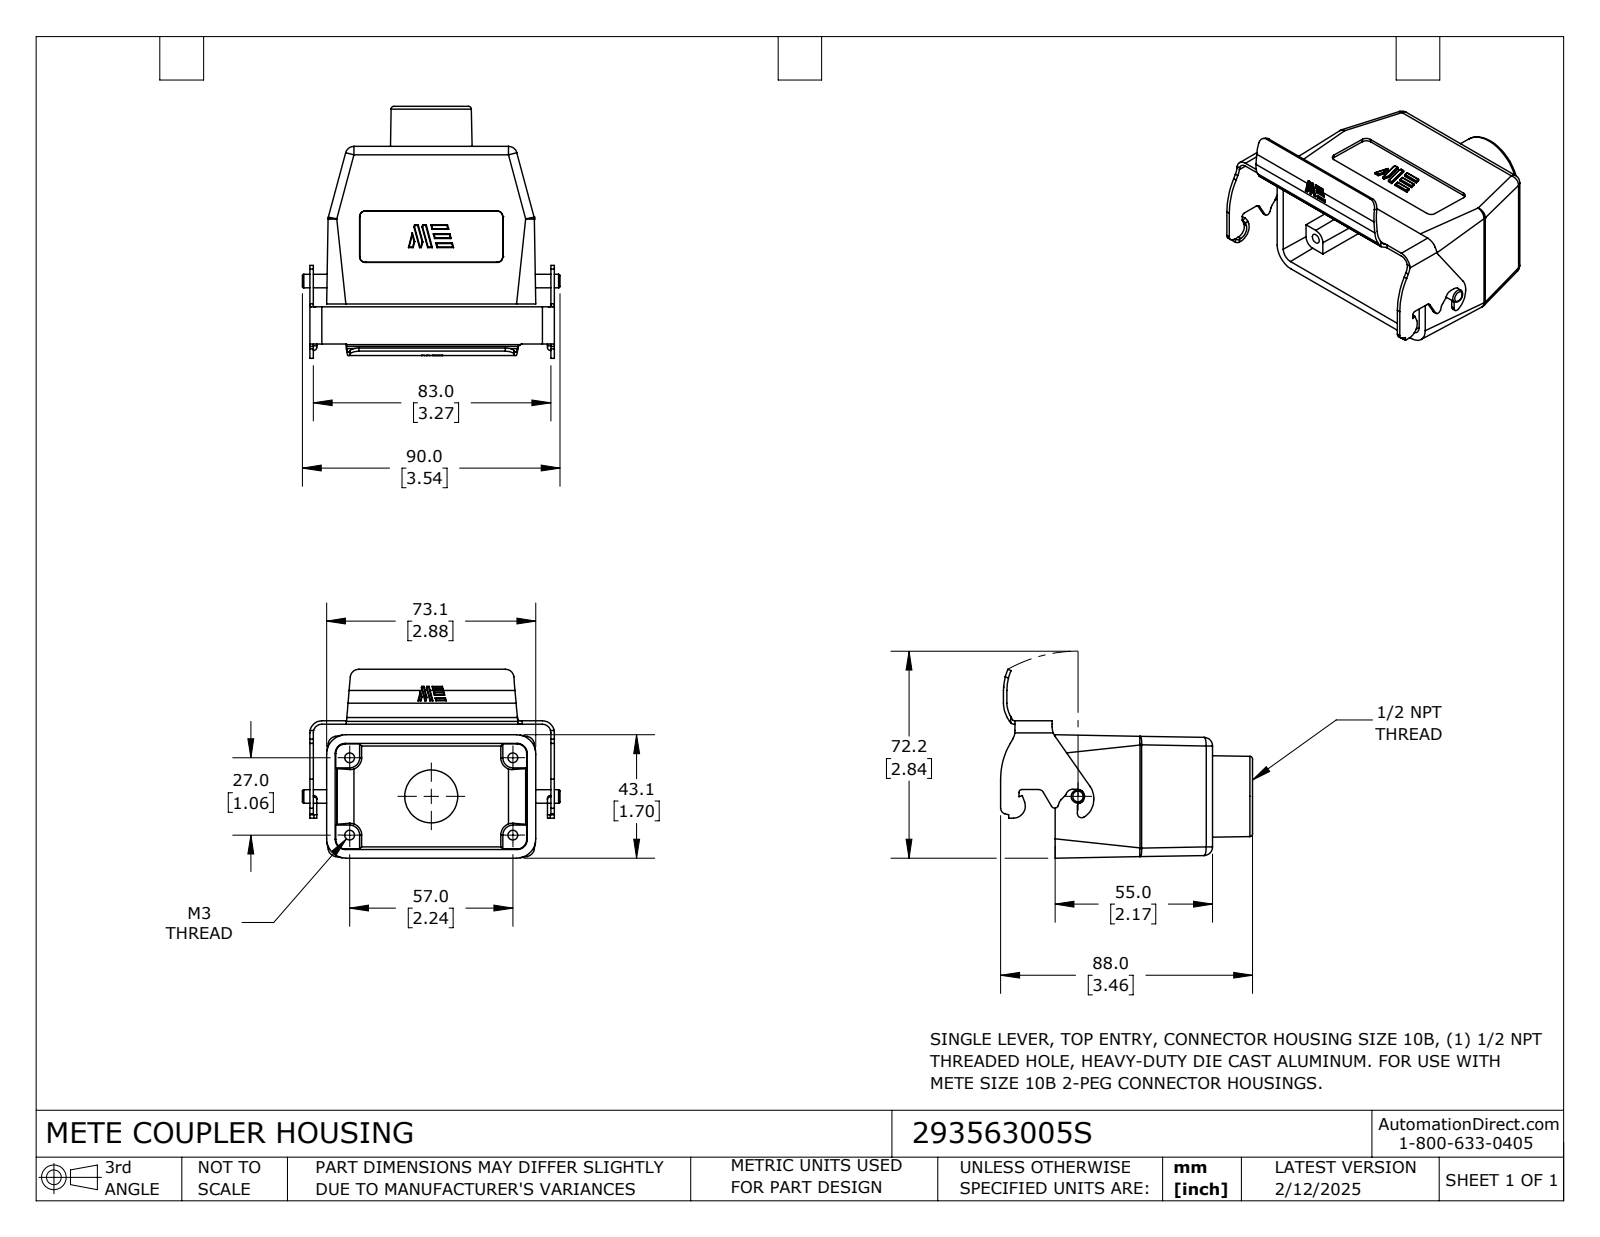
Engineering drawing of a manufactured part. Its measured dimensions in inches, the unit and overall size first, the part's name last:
Units: inches
Overall size (bounding box): 3.543 × 3.465 × 2.596
Round holes (diameter × count): ⌀0.134 ×4, ⌀0.728 ×1
Round bosses / shafts (diameter × count): ⌀0.185 ×1
Partial cylindrical surfaces — rounded edges, fillets, slot ends (radius × count): R0.008 ×55, R0.118 ×13, R0.039 ×12, R0.079 ×11, R0.098 ×5, R0.031 ×3, R0.165 ×3, R0.059 ×2
Main face-to-face distances: 0.118, 0.047, 0.04, 0.078, 0.447, 0.329, 3.315, 3.268, 2.047, 2.165
Hole centre spacings: 1.242, 1.063, 2.244, 2.483
Volume: 3.295 in³ · Surface area: 57.64 in²
Bodies: 1 solid, 406 faces (176 planar, 178 cylindrical, 52 other)
Part name (STEP PRODUCT): 293563005S
STEP written by: SolidWorks 2024 (CONFIG_CONTROL_DESIGN)
